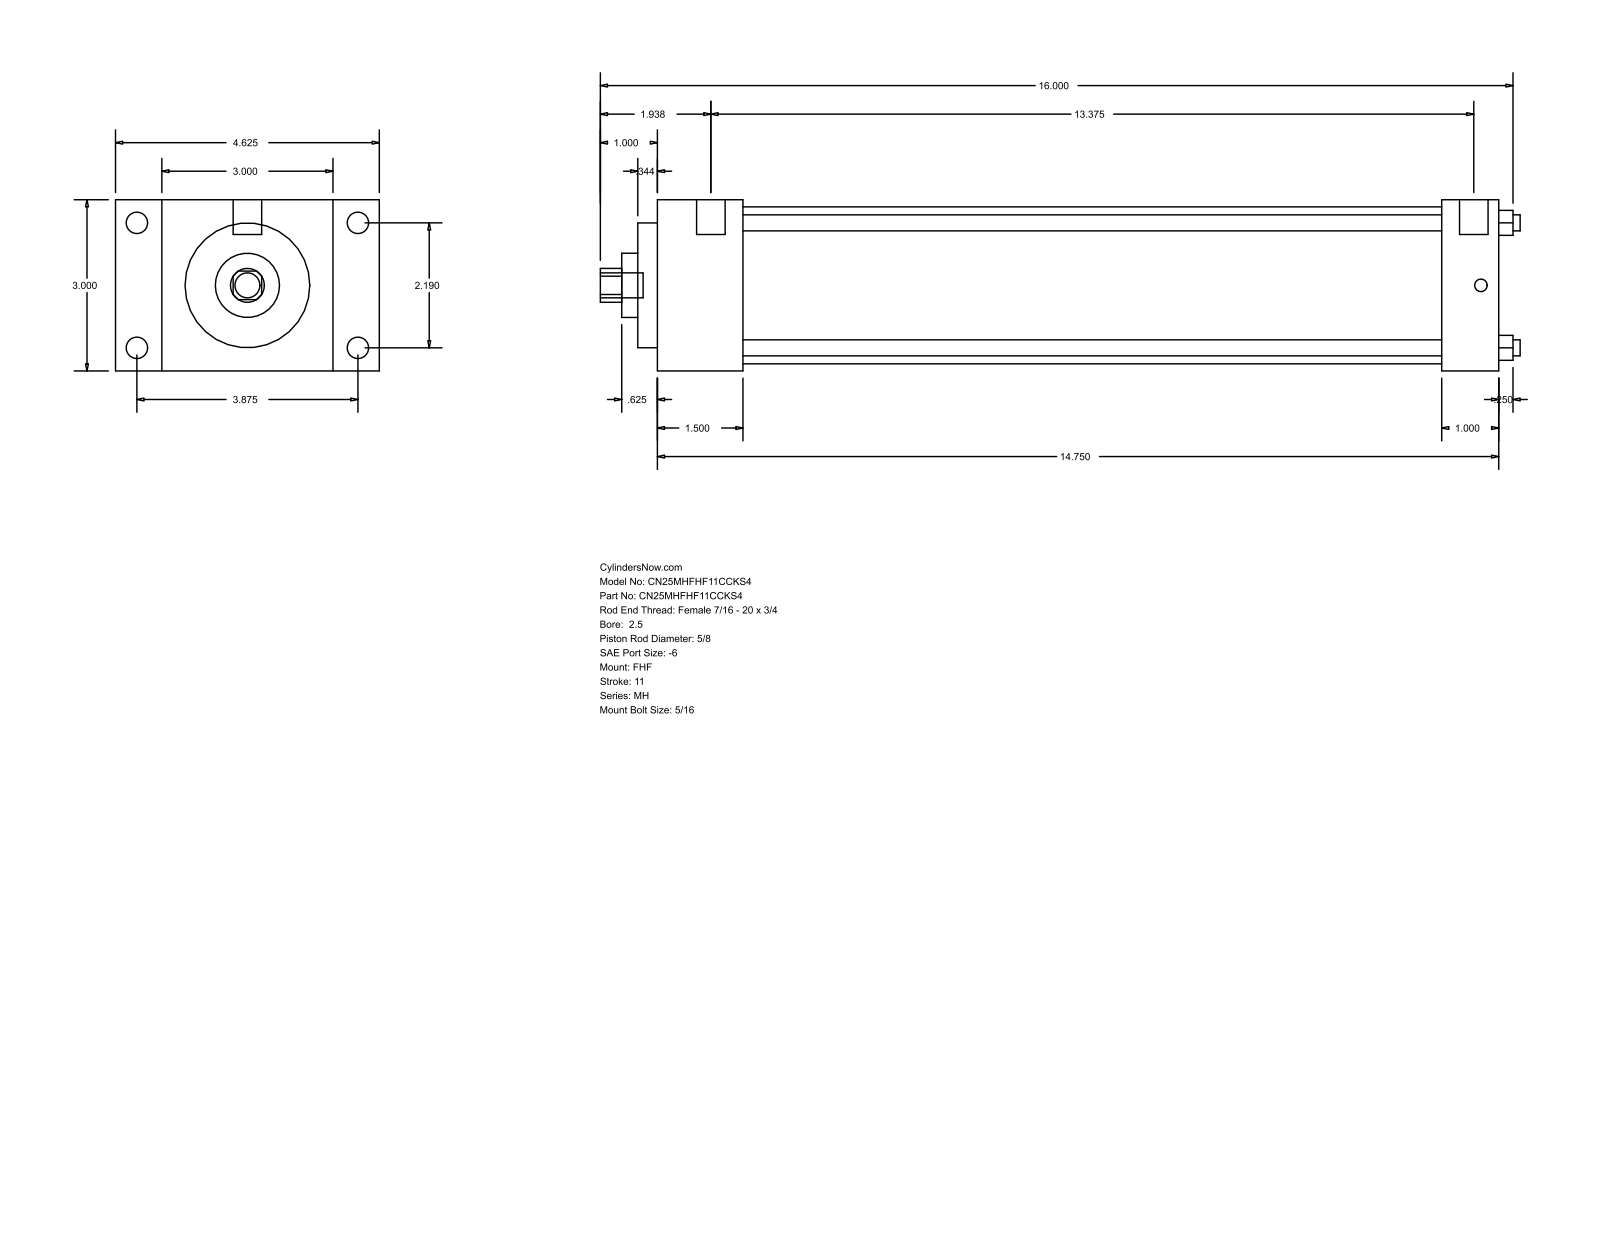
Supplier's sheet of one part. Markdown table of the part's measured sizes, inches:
| quantity | value |
| --- | --- |
| part name | MH_FHF__0250_0.625 |
| STEP written by | GSSL Pune (CONFIG_CONTROL_DESIGN) |
| units | inches |
| bodies | 0 solids, 90 faces (61 planar, 29 cylindrical, 0 other) |
| overall size | 16.125 × 4.625 × 3 |
| round holes (diameter × count) | 0.281 × 4, 0.625 × 1, 1.125 × 1, 2.187 × 1, 2.75 × 1 |
| round bosses / shafts (diameter × count) | 0.375 × 4, 0.219 × 4, 0.5 × 2, 0.437 × 1 |
| partial cylindrical surfaces (radius × count) | 0.297 × 1 |
| main face-to-face distances | 3, 14.75, 1.5, 13.25, 0.813, 3.813, 4.625, 1, 13.75, 12.25 |
| hole center spacings | 1.548, 2.19, 3.097 |
